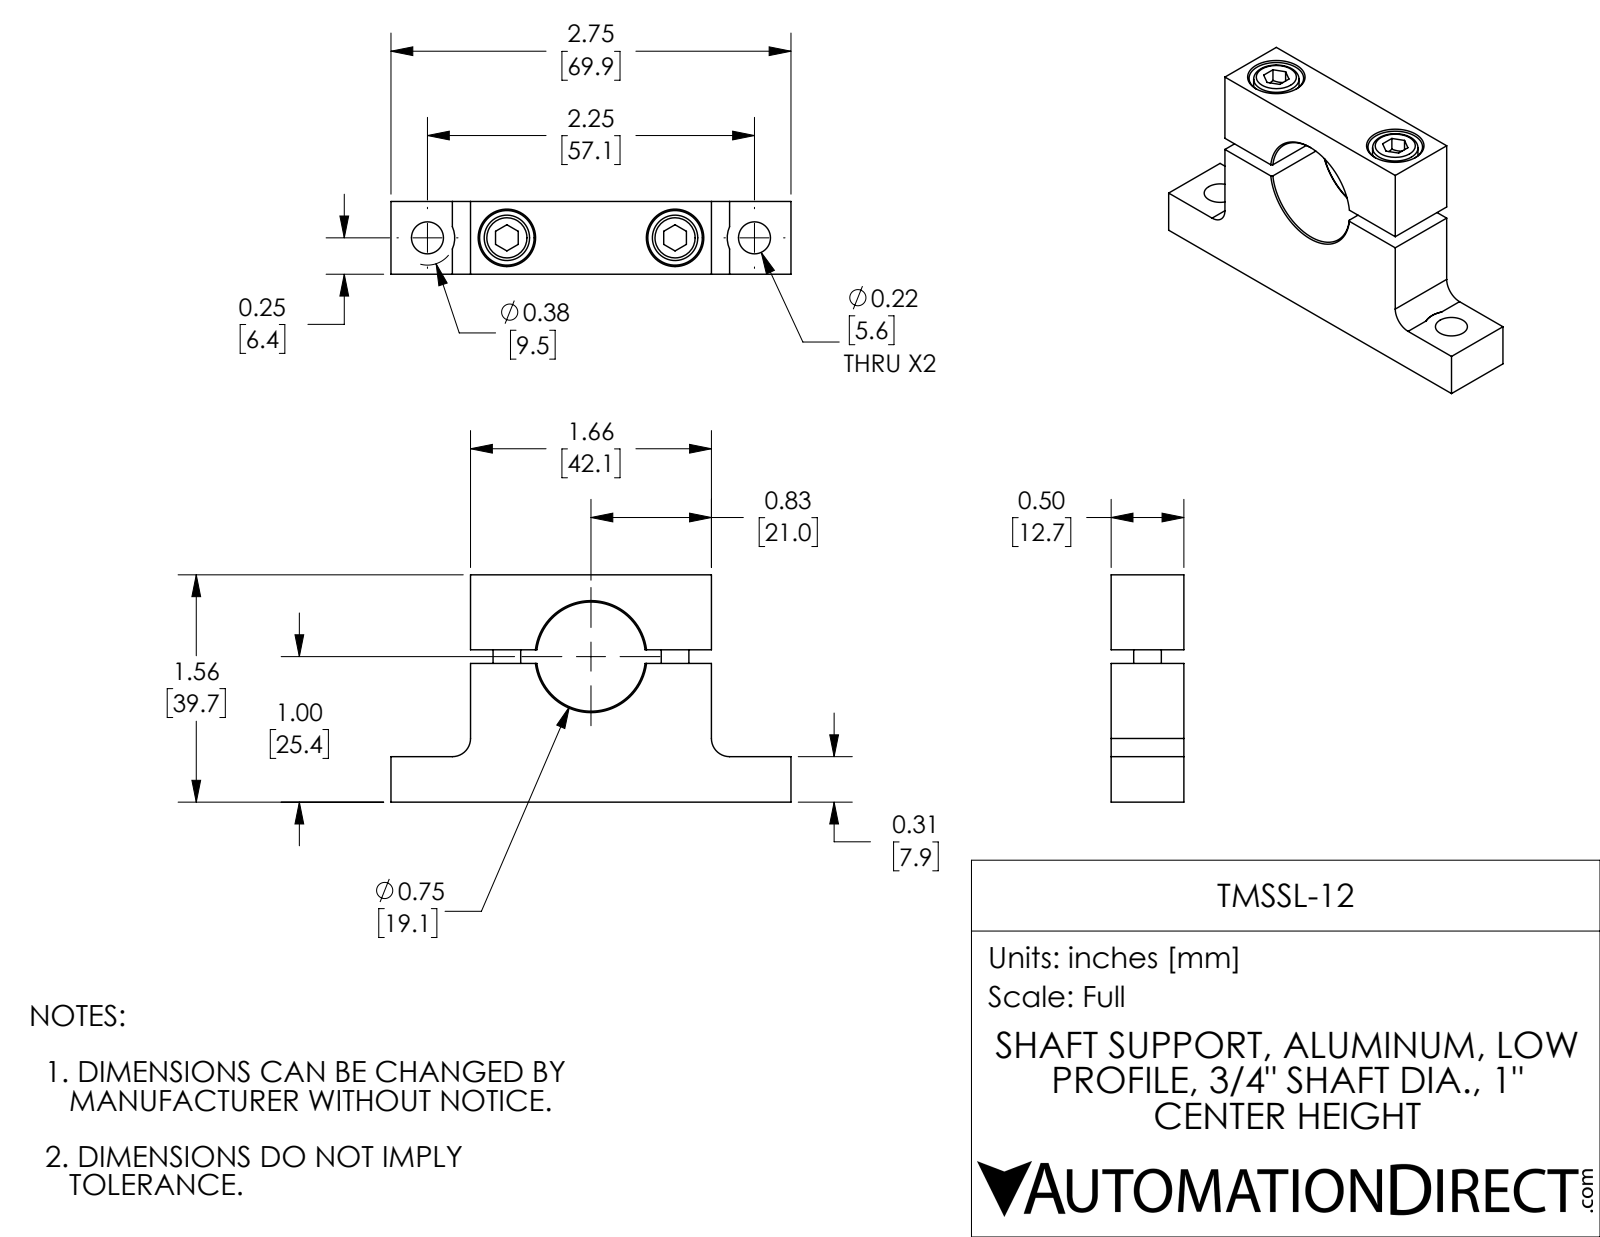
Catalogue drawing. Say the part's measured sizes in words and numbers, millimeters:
The part is named "TMSSL-12". Its 3-D file was written by "SolidWorks 2017 (AUTOMOTIVE_DESIGN)". It is 4 solids with 93 faces: 38 planar, 31 cylindrical and 24 other. Overall it measures 69.9 by 39.7 by 12.7 millimeters. Its volume is 18 890 cubic millimeters and its surface area 9 290 square millimeters. Round holes: 2 of diameter 3.7, 2 of diameter 5.1, 2 of diameter 5.6, 2 of diameter 9.5, 1 of diameter 19.1. Round bosses or shafts: 2 of diameter 7.9, 2 of diameter 4.8. Partial cylindrical surfaces (rounded edges, fillets, slot ends): 2 of radius 3.2, 1 of radius 4.7, 1 of radius 4.8. The main face-to-face distances are 12.7, 39.7, 42.1, 24.2, 15.5, 26.6, 2.4, 13.1, 8, 16.3. The hole center spacings are 13.9, 43.2, 29.4, 57.1.
